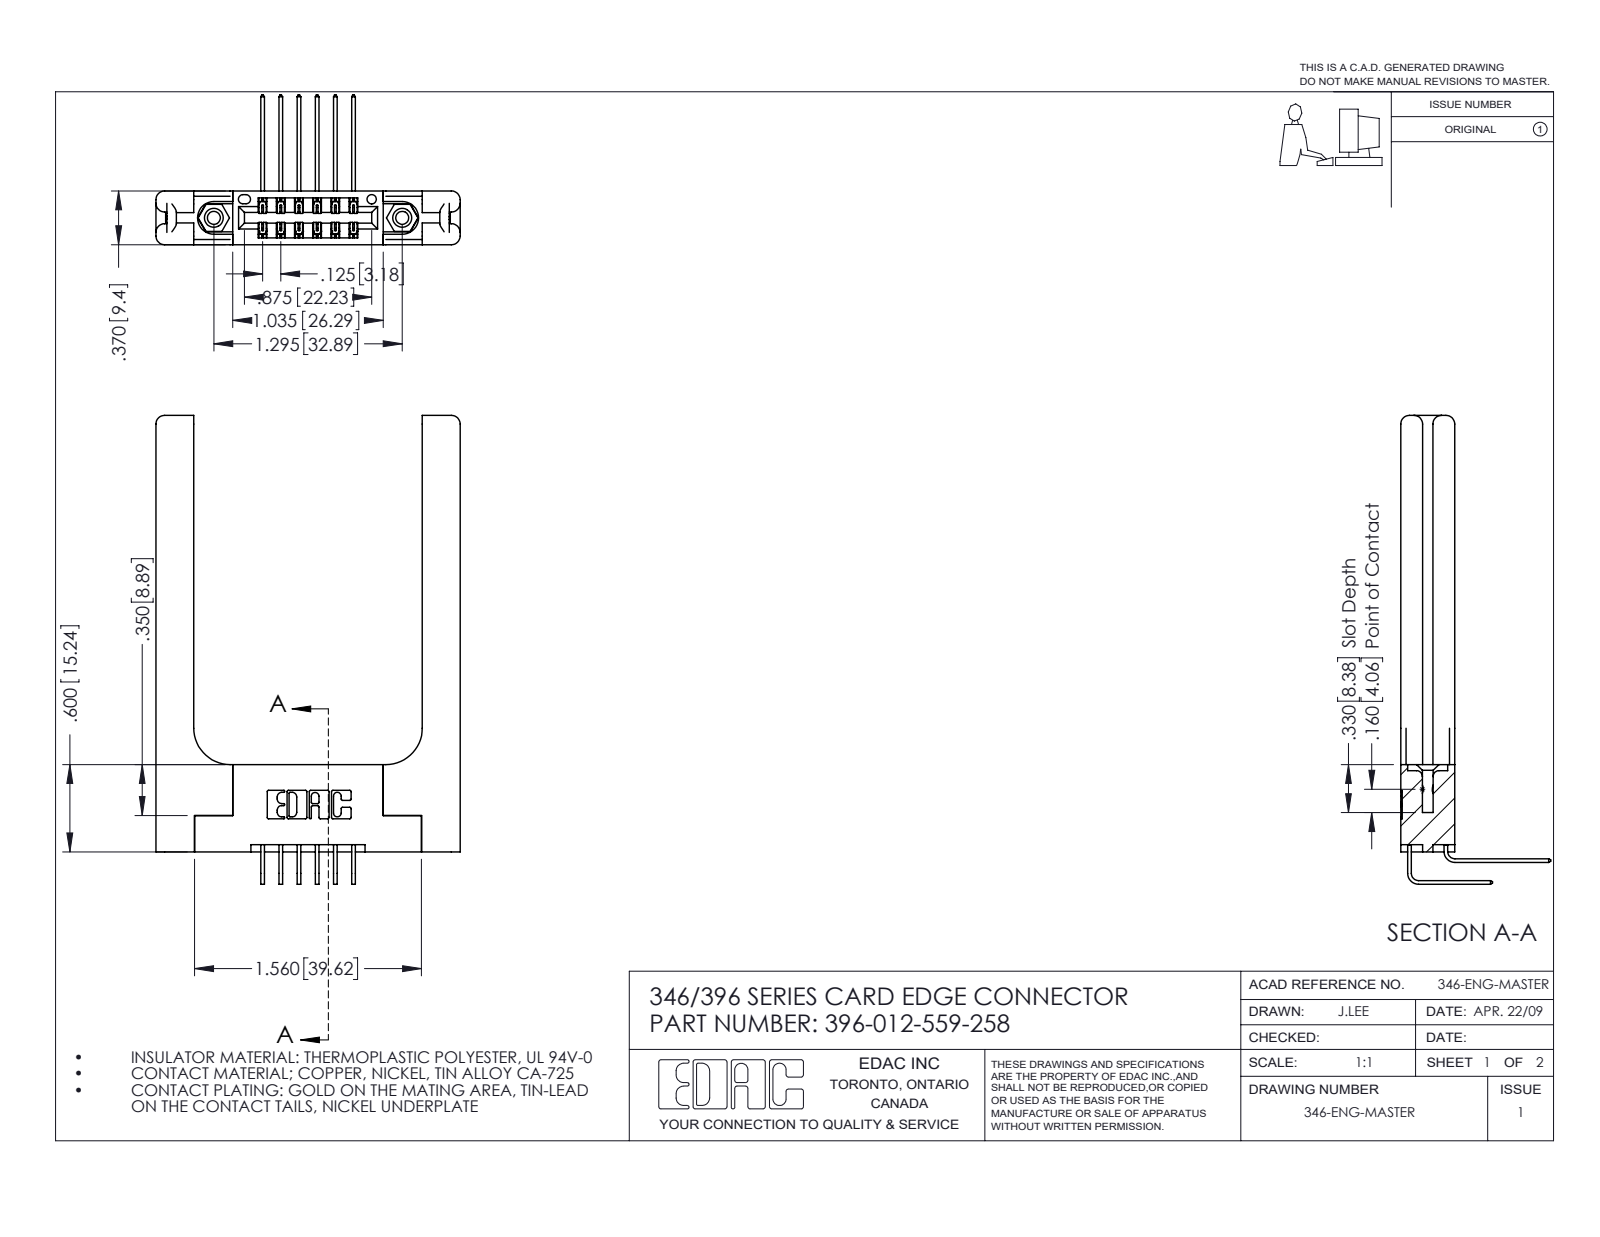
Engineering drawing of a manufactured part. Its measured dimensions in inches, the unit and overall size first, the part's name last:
Units: inches
Overall size (bounding box): 3.223 × 2.091 × 1.03
Round holes (diameter × count): ⌀0.089 ×2, ⌀0.125 ×2, ⌀0.156 ×2, ⌀0.064 ×1
Round bosses / shafts (diameter × count): ⌀0.155 ×2
Partial cylindrical surfaces — rounded edges, fillets, slot ends (radius × count): R0.01 ×22, R0.006 ×18, R0.06 ×16, R0.007 ×6, R0.031 ×6, R0.026 ×3, R0.014 ×2, R0.022 ×2
Main face-to-face distances: 0.37, 0.15, 0.22, 0.072, 0.25, 0.148, 0.048, 0.322, 1.571, 0.025
Hole centre spacings: 0.246, 1.092, 1.295
Volume: 0.761 in³ · Surface area: 17.93 in²
Bodies: 17 solids, 1026 faces (668 planar, 298 cylindrical, 60 other)
Part name (STEP PRODUCT): 346-220-058_345-220-058; 346 Part_Flush Mounting Lugs - 0.156 Dia-TH; 345-292-001_558 559 Tail - 1; 345-292-001_559 Tail - 2 (+2 more)
STEP written by: SolidWorks 2016 (CONFIG_CONTROL_DESIGN)
